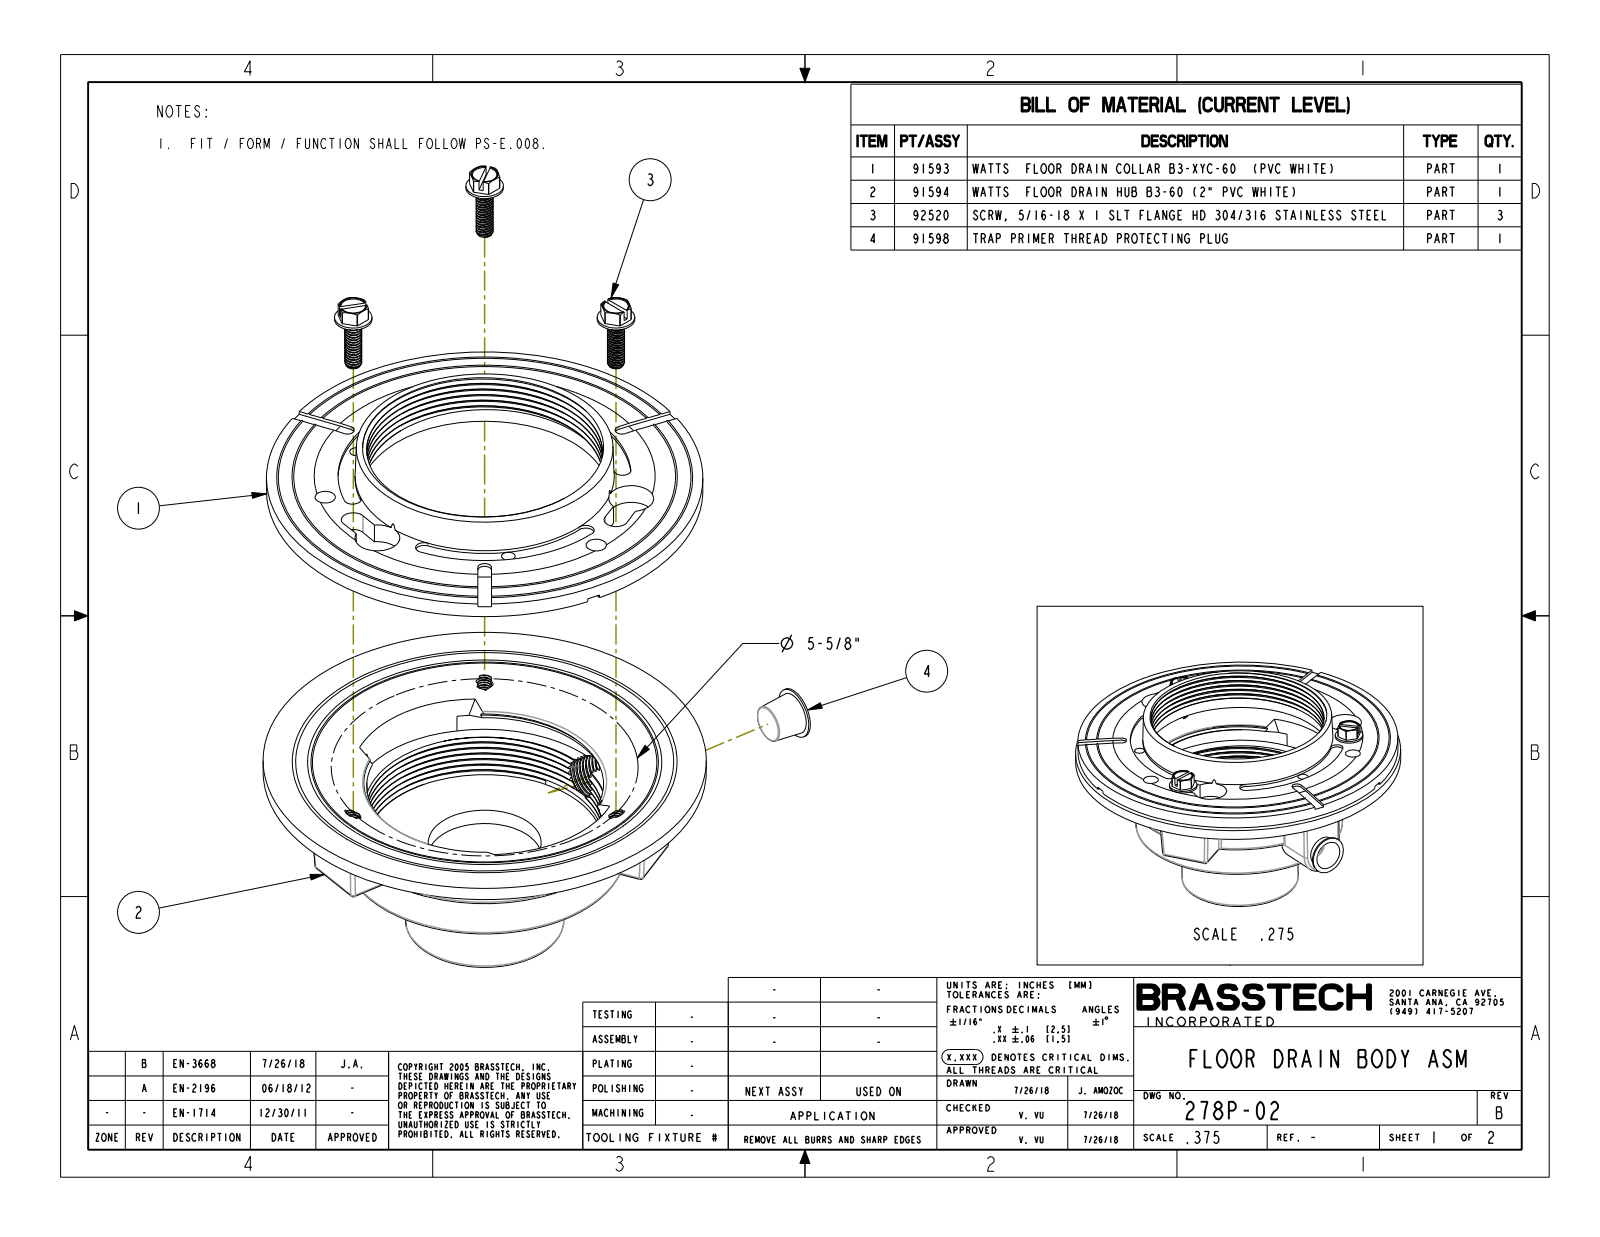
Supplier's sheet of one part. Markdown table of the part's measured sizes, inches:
| quantity | value |
| --- | --- |
| part name | 91593; 91594; 92520; 91598 (+1 more) |
| STEP written by | PRO/ENGINEER BY PARAMETRIC TECHNOLOGY CORPORATION, 2013150 (CONFIG_CONTROL_DESIGN) |
| units | inches |
| bodies | 6 solids, 1210 faces (141 planar, 522 cylindrical, 547 other) |
| overall size | 8.125 × 8.125 × 4.65 |
| volume | 38.92 in³ |
| surface area | 332.1 in² |
| round holes (diameter × count) | 0.257 × 6, 0.25 × 3, 0.37 × 3, 0.82 × 3, 4.325 × 2, 0.703 × 1, 2.07 × 1, 2.4 × 1, 4.531 × 1 |
| round bosses / shafts (diameter × count) | 0.268 × 51, 0.687 × 3, 0.313 × 3, 0.308 × 3, 8.125 × 1, 8 × 1, 5.16 × 1, 2.9 × 1 |
| partial cylindrical surfaces (radius × count) | 0.06 × 17, 0.125 × 6, 0.134 × 6, 0.156 × 6, 0.02 × 4, 0.219 × 3, 0.286 × 3, 2.34 × 2 |
| main face-to-face distances | 0.25, 1.85, 2.1, 2.475, 2.225, 0.375, 0.062, 0.313, 1.04, 0.79 |
| hole center spacings | 2.781, 2.5, 2.781, 3, 1.634, 2.813, 3.804, 4.33 |
